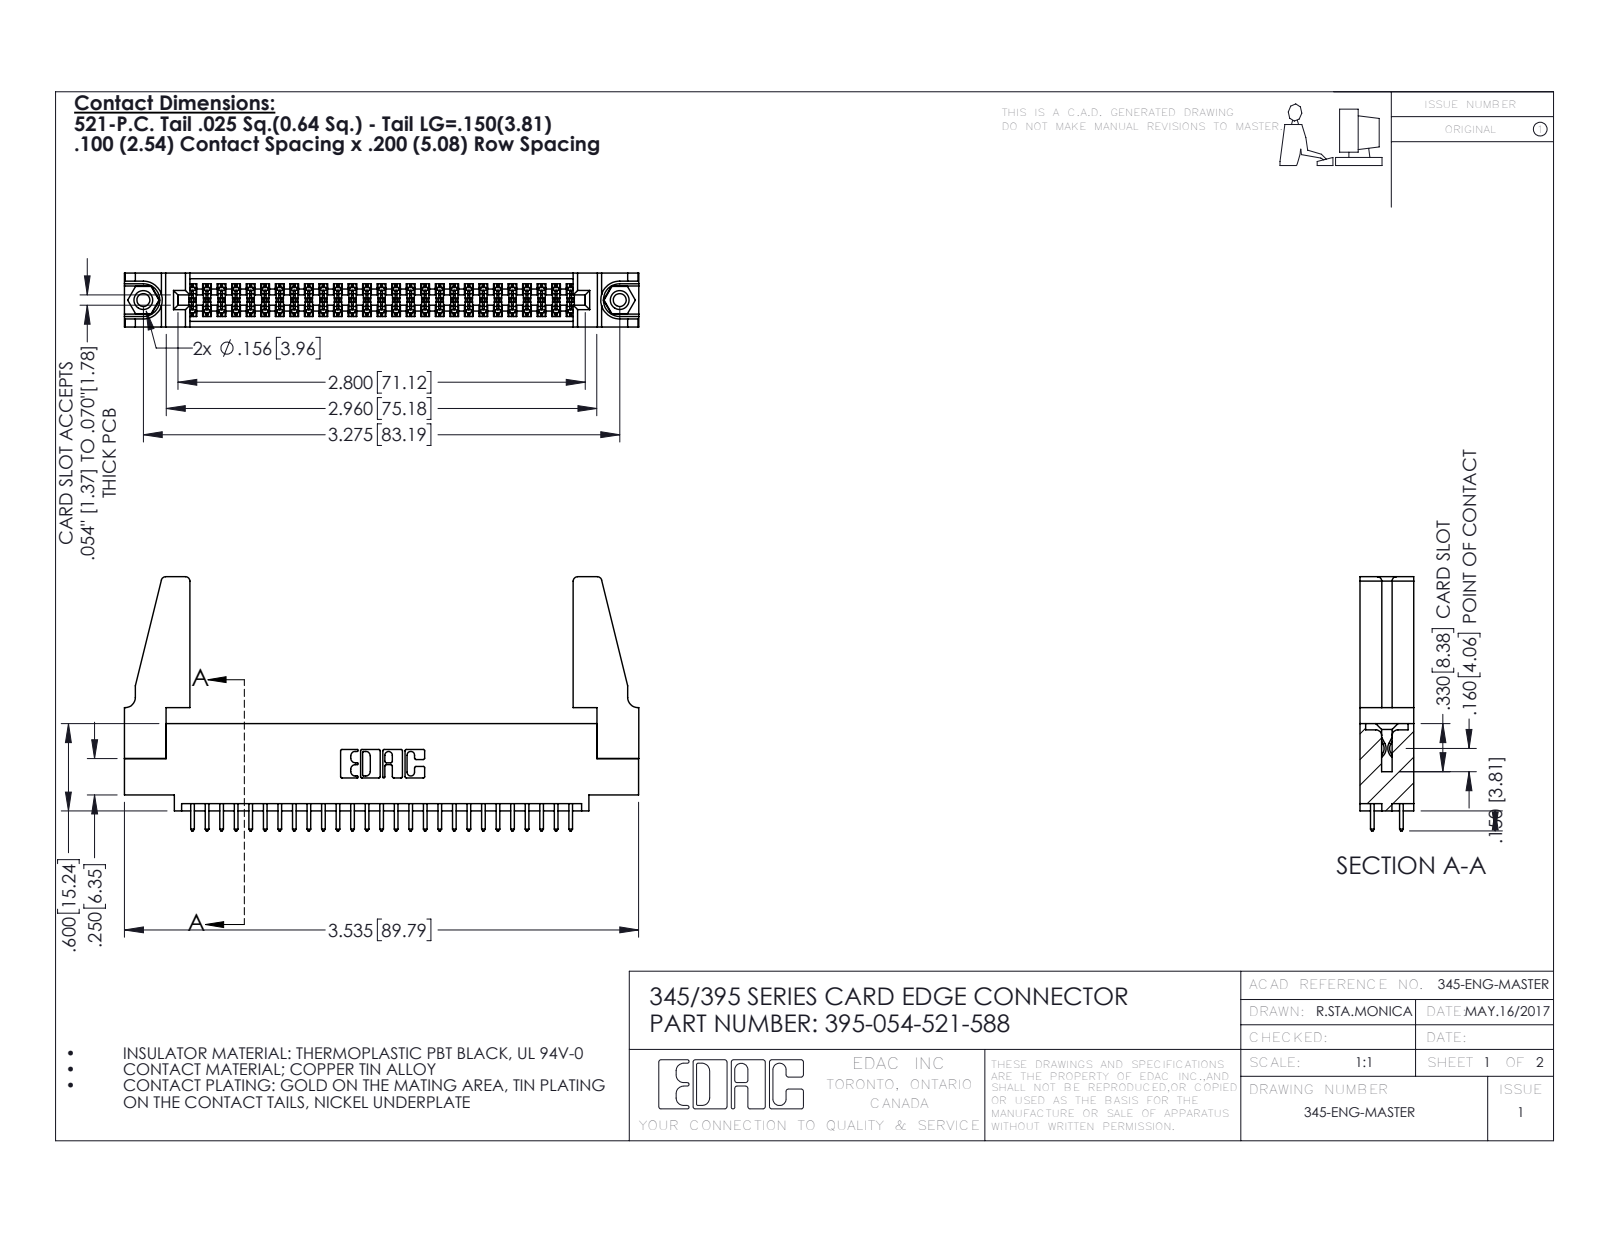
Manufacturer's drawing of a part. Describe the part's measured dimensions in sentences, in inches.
The part is named "345-250-001_345-250-001-102; 345-292-001_345-293-121; 395-054-521-588; 345 Part_0.110 Offset - 0.156 Dia-TH (+1 more)". Its 3-D file was written by "SolidWorks 2016 (CONFIG_CONTROL_DESIGN)". It is 59 solids with 2954 faces: 1938 planar, 1000 cylindrical and 16 other. Overall it measures 3.536 by 1.747 by 0.37 inches. Its volume is 0.717 cubic inches and its surface area 23.76 square inches. Round holes: 2 of diameter 0.089, 2 of diameter 0.125, 2 of diameter 0.156, 1 of diameter 0.064. Round bosses or shafts: 2 of diameter 0.155. Partial cylindrical surfaces (rounded edges, fillets, slot ends): 81 of radius 0.006, 54 of radius 0.01, 22 of radius 0.01, 8 of radius 0.03, 6 of radius 0.007, 6 of radius 0.031, 3 of radius 0.026, 2 of radius 0.014. The main face-to-face distances are 0.072, 0.298, 0.37, 0.2, 0.098, 0.272, 0.025, 0.225, 0.175, 0.149. The hole center spacings are 0.27, 3.04, 3.275.
